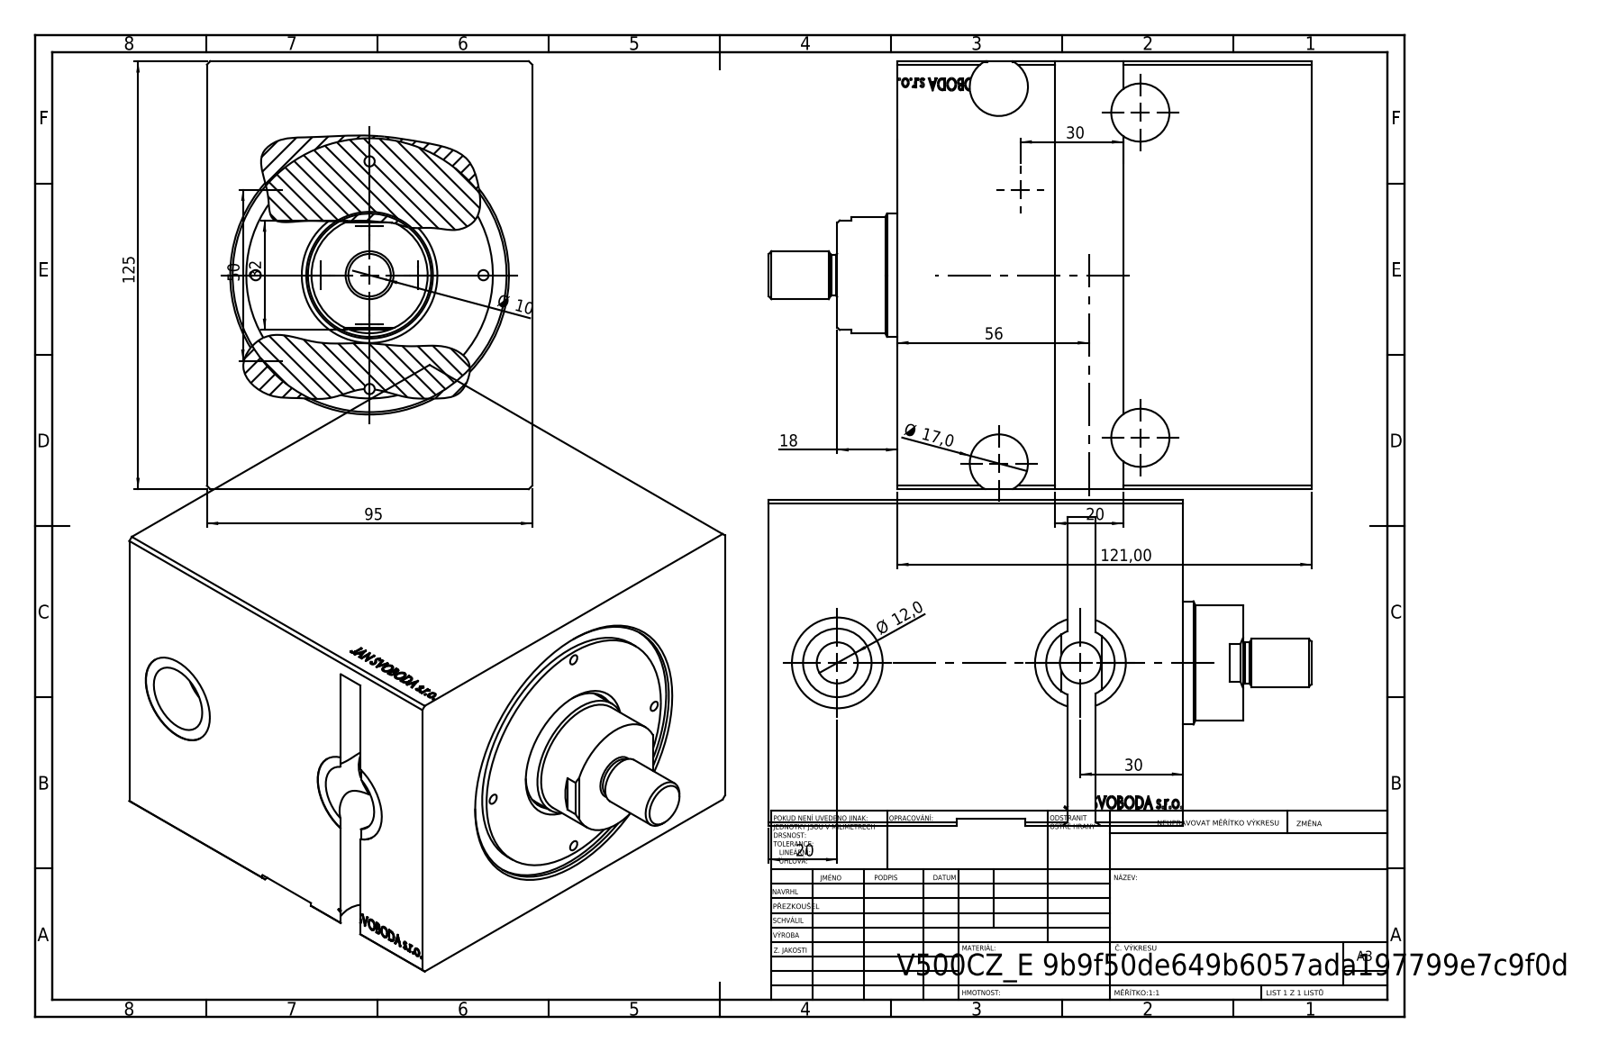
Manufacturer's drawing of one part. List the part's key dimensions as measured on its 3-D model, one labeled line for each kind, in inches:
Part name (STEP PRODUCT): V500CZ_VC_vysunovaci_E; V500CZ_FM; V500CZ_E; V500CZ_VCP_E
STEP written by: SolidWorks 2019 (CONFIG_CONTROL_DESIGN)
Units: inches
Bodies: 6 solids, 753 faces (328 planar, 58 cylindrical, 367 other)
Overall size (bounding box): 6.24 × 4.921 × 3.74
Volume: 79.57 in³ · Surface area: 216.6 in²
Round holes (diameter × count): ⌀0.118 ×4, ⌀0.669 ×4, ⌀0.472 ×2, ⌀1.043 ×2, ⌀0.394 ×1, ⌀0.787 ×1, ⌀1.417 ×1, ⌀1.457 ×1, ⌀2.48 ×1, ⌀3.15 ×1
Round bosses / shafts (diameter × count): ⌀2.835 ×1, ⌀1.335 ×1, ⌀0.551 ×1, ⌀0.472 ×1
Partial cylindrical surfaces — rounded edges, fillets, slot ends (radius × count): R0.394 ×1
Main face-to-face distances: 3.74, 4.921, 4.764, 2.205, 2.559, 0.465, 2.094, 4.299, 0.071, 0.394
Hole centre spacings: 1.309, 1.851, 1.654, 2.618, 4.351, 2.795, 3.74, 4.331
